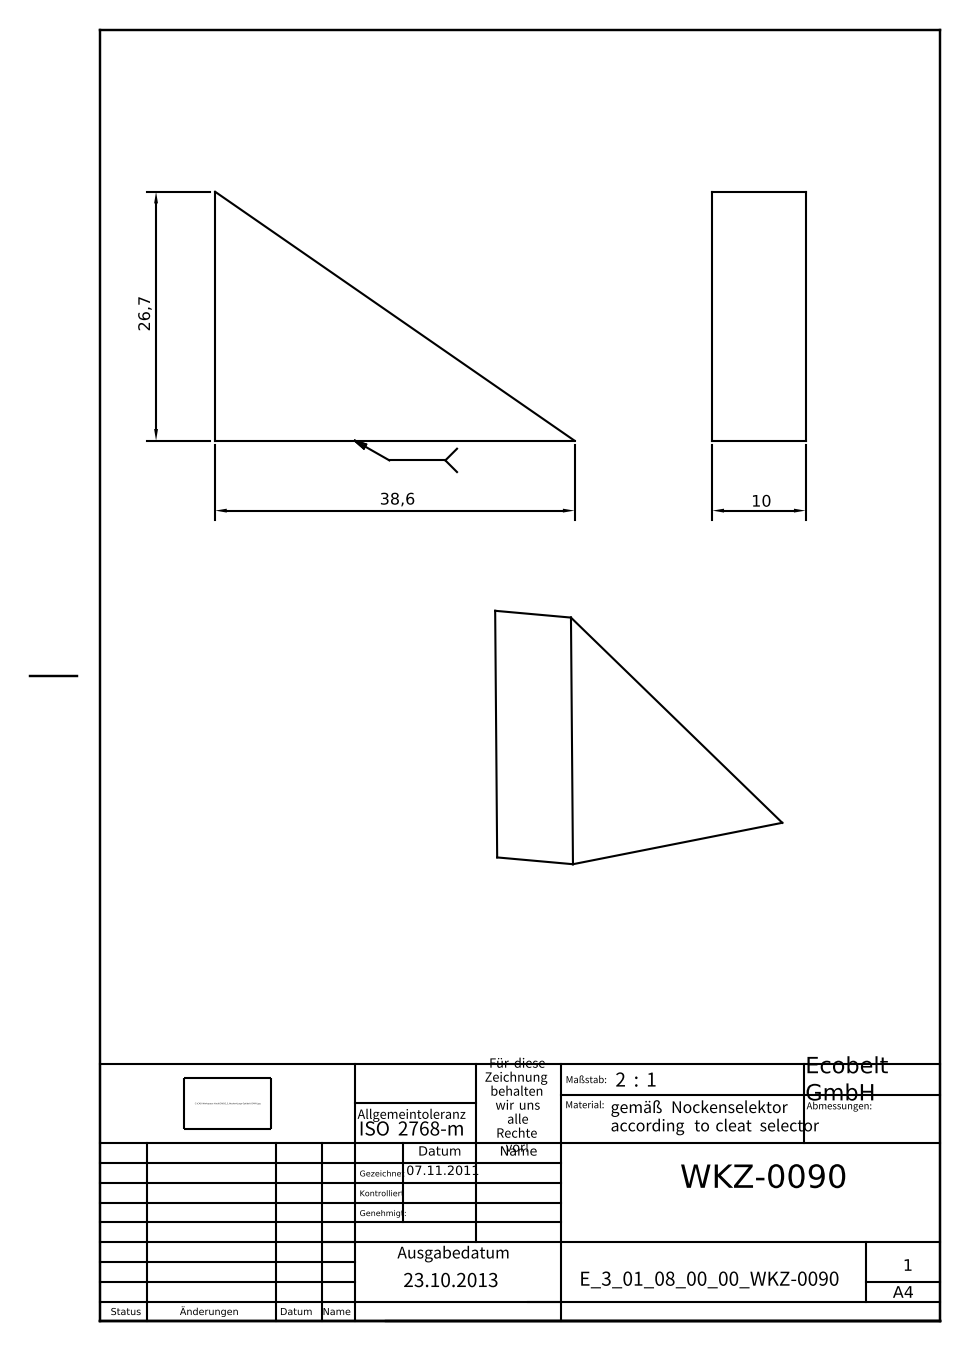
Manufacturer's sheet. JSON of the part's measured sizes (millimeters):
{"part_name": "E_3_01_08_00_00_WKZ-0090", "step_written_by": "Autodesk Inventor 2025 (AUTOMOTIVE_DESIGN)", "units": "millimeters", "bodies": {"solids": 1, "faces": 5, "planar": 5, "cylindrical": 0, "other": 0}, "overall_size": [38.55, 26.7, 10], "volume_mm3": 5146, "surface_area_mm2": 2151, "face_to_face_distances": [10]}
